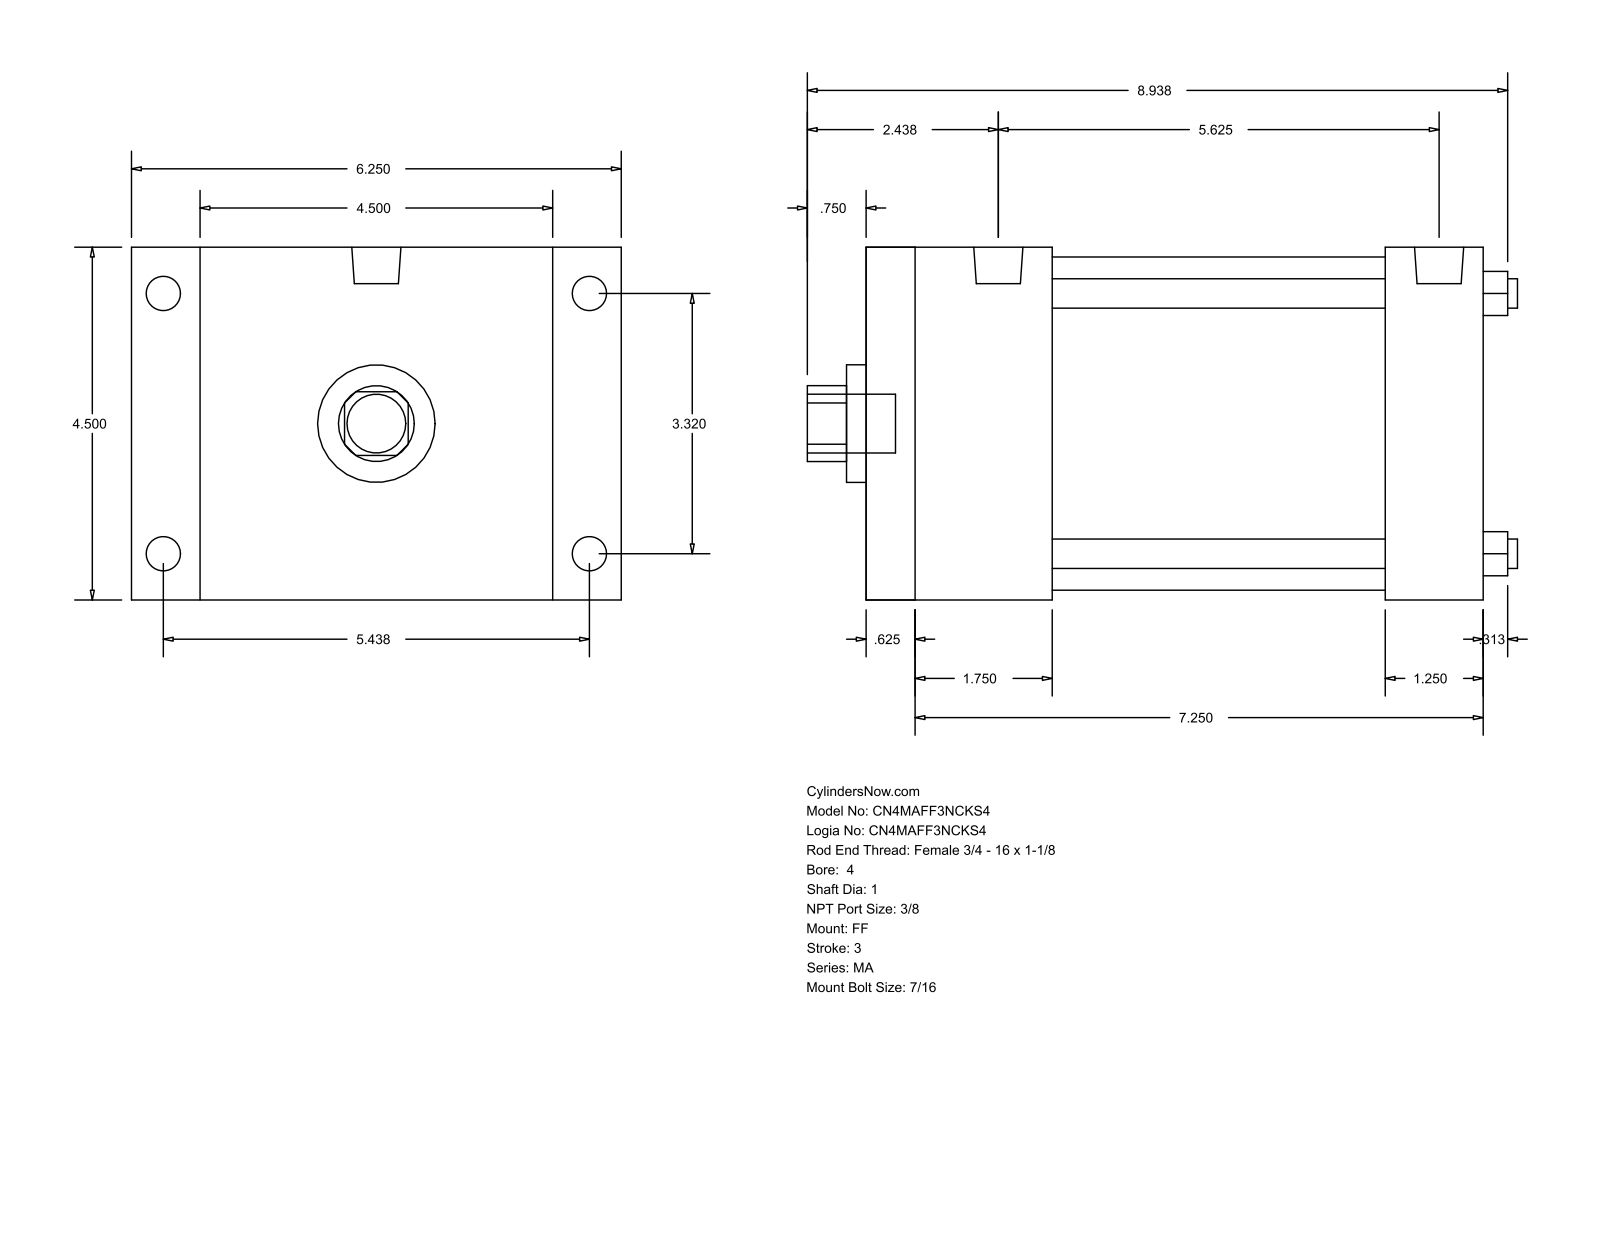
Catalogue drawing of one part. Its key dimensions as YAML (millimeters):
part_name: "MA_FF__0400_1"
step_written_by: "GSSL Pune (CONFIG_CONTROL_DESIGN)"
units: millimeters
bodies: {solids: 0, faces: 92, planar: 64, cylindrical: 28, other: 0}
overall_size: [230.19, 158.75, 114.3]
round_holes:
  - {diameter: 9.53, count: 4}
  - {diameter: 25.4, count: 1}
  - {diameter: 38.1, count: 1}
  - {diameter: 107.95, count: 1}
round_bosses_or_shafts:
  - {diameter: 11.11, count: 8}
  - {diameter: 15.93, count: 2}
  - {diameter: 19.05, count: 1}
partial_cylinders:
  - {radius: 12.29, count: 1}
face_to_face_distances: [114.3, 200.02, 15.87, 184.15, 22.23, 136.53, 168.27, 152.4, 31.75, 60.33]
hole_center_spacings: [59.62, 84.32, 119.25]
